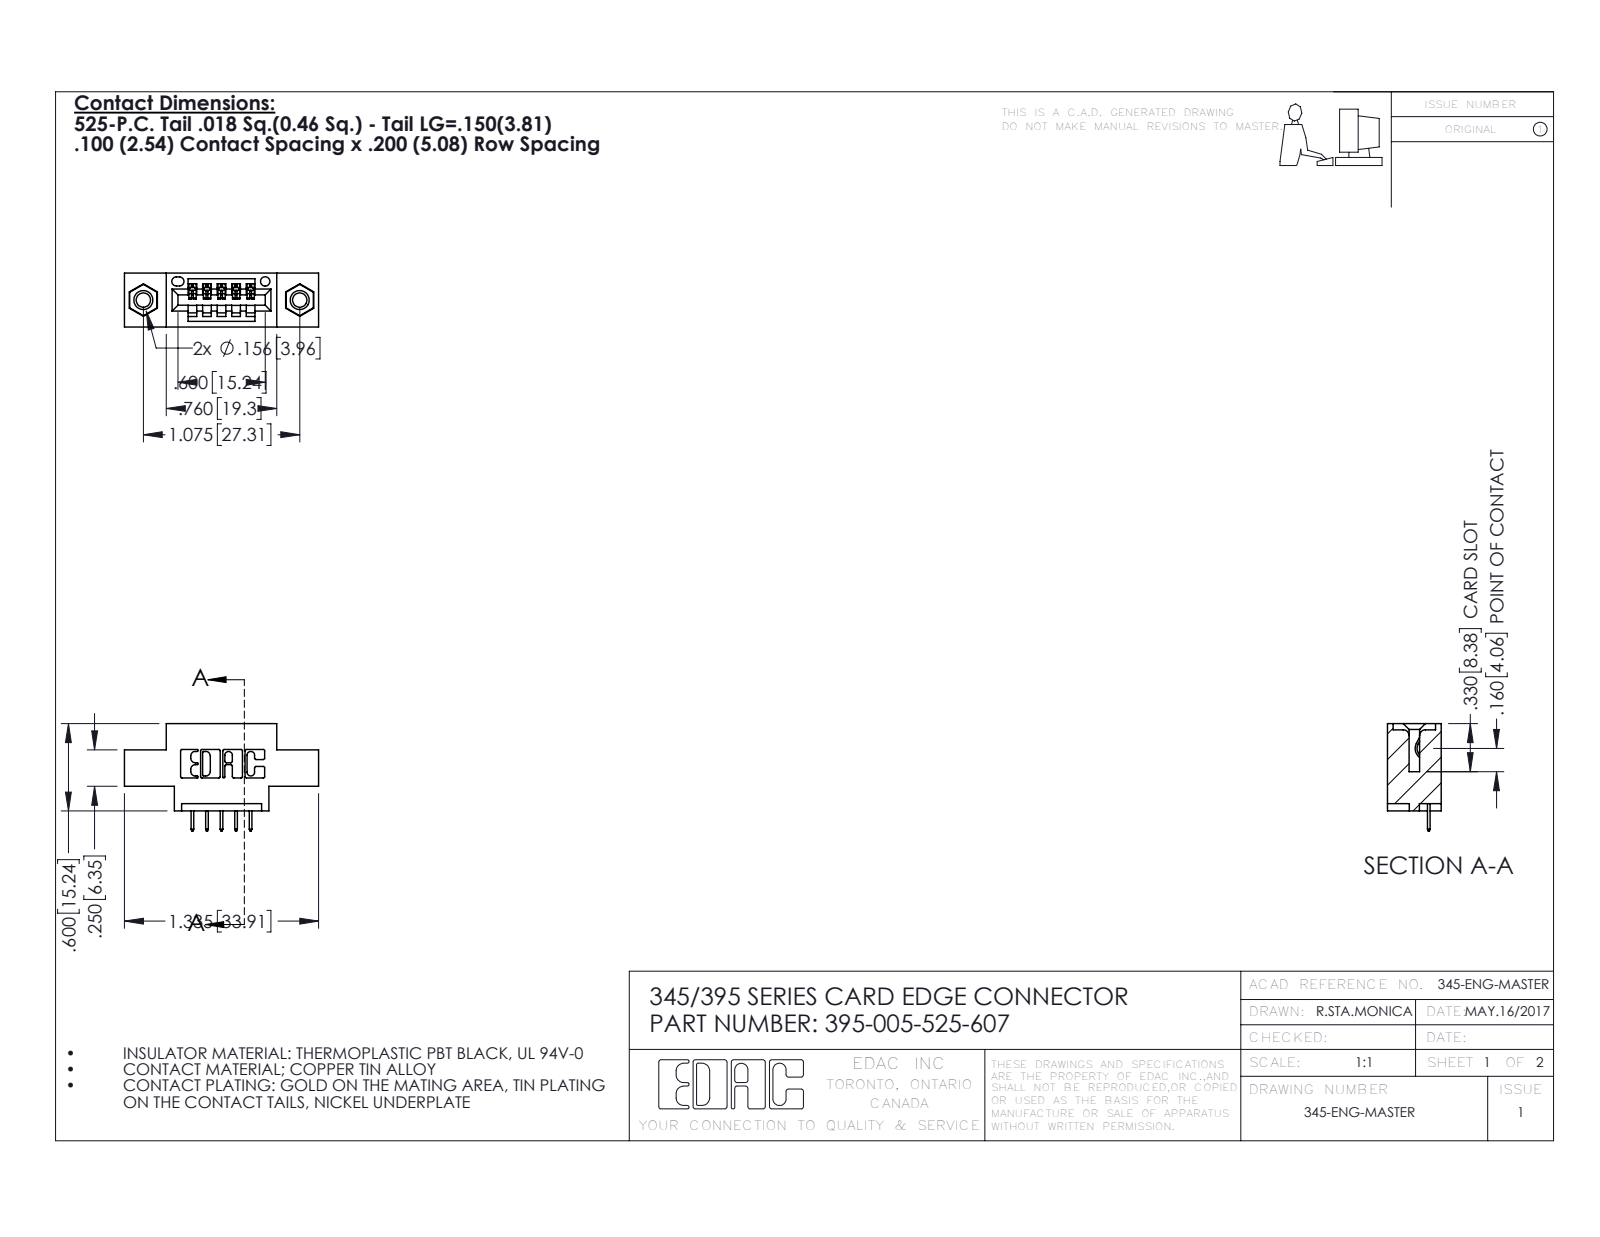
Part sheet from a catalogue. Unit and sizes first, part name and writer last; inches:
Units: inches
Overall size (bounding box): 1.335 × 0.737 × 0.37
Round holes (diameter × count): ⌀0.098 ×2, ⌀0.125 ×2, ⌀0.156 ×2, ⌀0.064 ×1
Round bosses / shafts (diameter × count): ⌀0.155 ×2
Partial cylindrical surfaces — rounded edges, fillets, slot ends (radius × count): R0.01 ×22, R0.006 ×10, R0.007 ×6, R0.031 ×6, R0.026 ×3, R0.031 ×2, R0.04 ×2, R0.014 ×1
Main face-to-face distances: 0.37, 0.2, 0.1, 0.072, 0.298, 0.025, 0.25, 0.06, 0.55, 0.15
Hole centre spacings: 0.27, 0.847, 1.075
Volume: 0.169 in³ · Surface area: 5.068 in²
Bodies: 8 solids, 500 faces (346 planar, 138 cylindrical, 16 other)
Part name (STEP PRODUCT): 345-250-001_345-250-005-103; 395-005-525-607; 345 Part_0.170 Offset - 0.156 Dia-TI; 345-292-001_345-293-125
STEP written by: SolidWorks 2020 (CONFIG_CONTROL_DESIGN)
